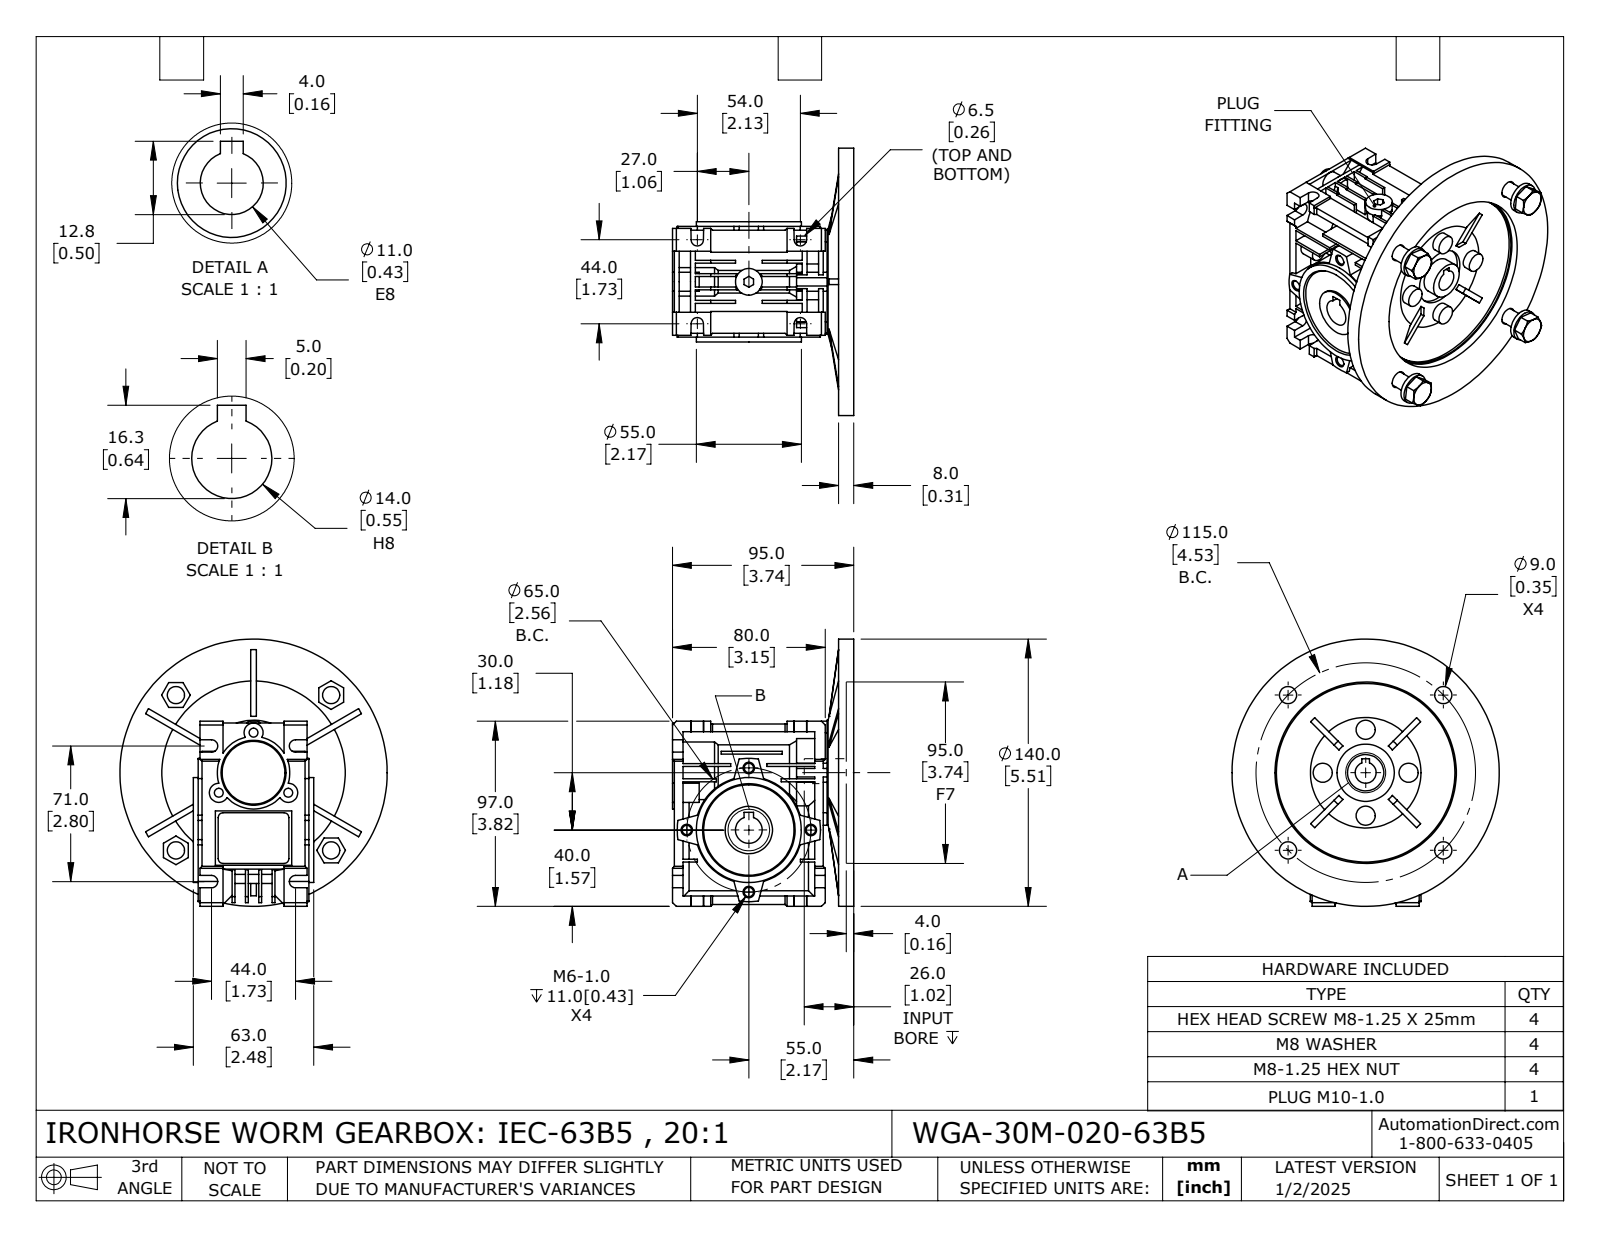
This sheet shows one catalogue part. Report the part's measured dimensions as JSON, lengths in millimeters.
{"part_name": "WGA-30M-020-63B5", "step_written_by": "SolidWorks 2024 (CONFIG_CONTROL_DESIGN)", "units": "millimeters", "bodies": {"solids": 6, "faces": 836, "planar": 542, "cylindrical": 216, "other": 78}, "overall_size": [140, 140, 95], "volume_mm3": 391916, "surface_area_mm2": 131275, "round_holes": [[9, 5], [4.92, 4], [4.65, 3], [4.92, 2], [11, 1], [11.5, 1], [14, 1], [14.5, 1], [19, 1], [24.8, 1], [30, 1], [93.5, 1]], "round_bosses_or_shafts": [[10, 4], [55, 2], [140, 1], [56, 1], [38, 1], [37, 1], [14, 1], [12, 1]], "partial_cylinders_radius": [[3.25, 8], [2.5, 4], [5, 3], [7.5, 1], [17, 1], [21.5, 1], [37.5, 1]], "face_to_face_distances": [8, 1.5, 7, 5.5, 1, 14, 4.5, 2, 8.5, 4], "hole_center_spacings": [32.5, 45.96, 57.5, 81.32, 21, 36.37, 37.61, 45.16]}
